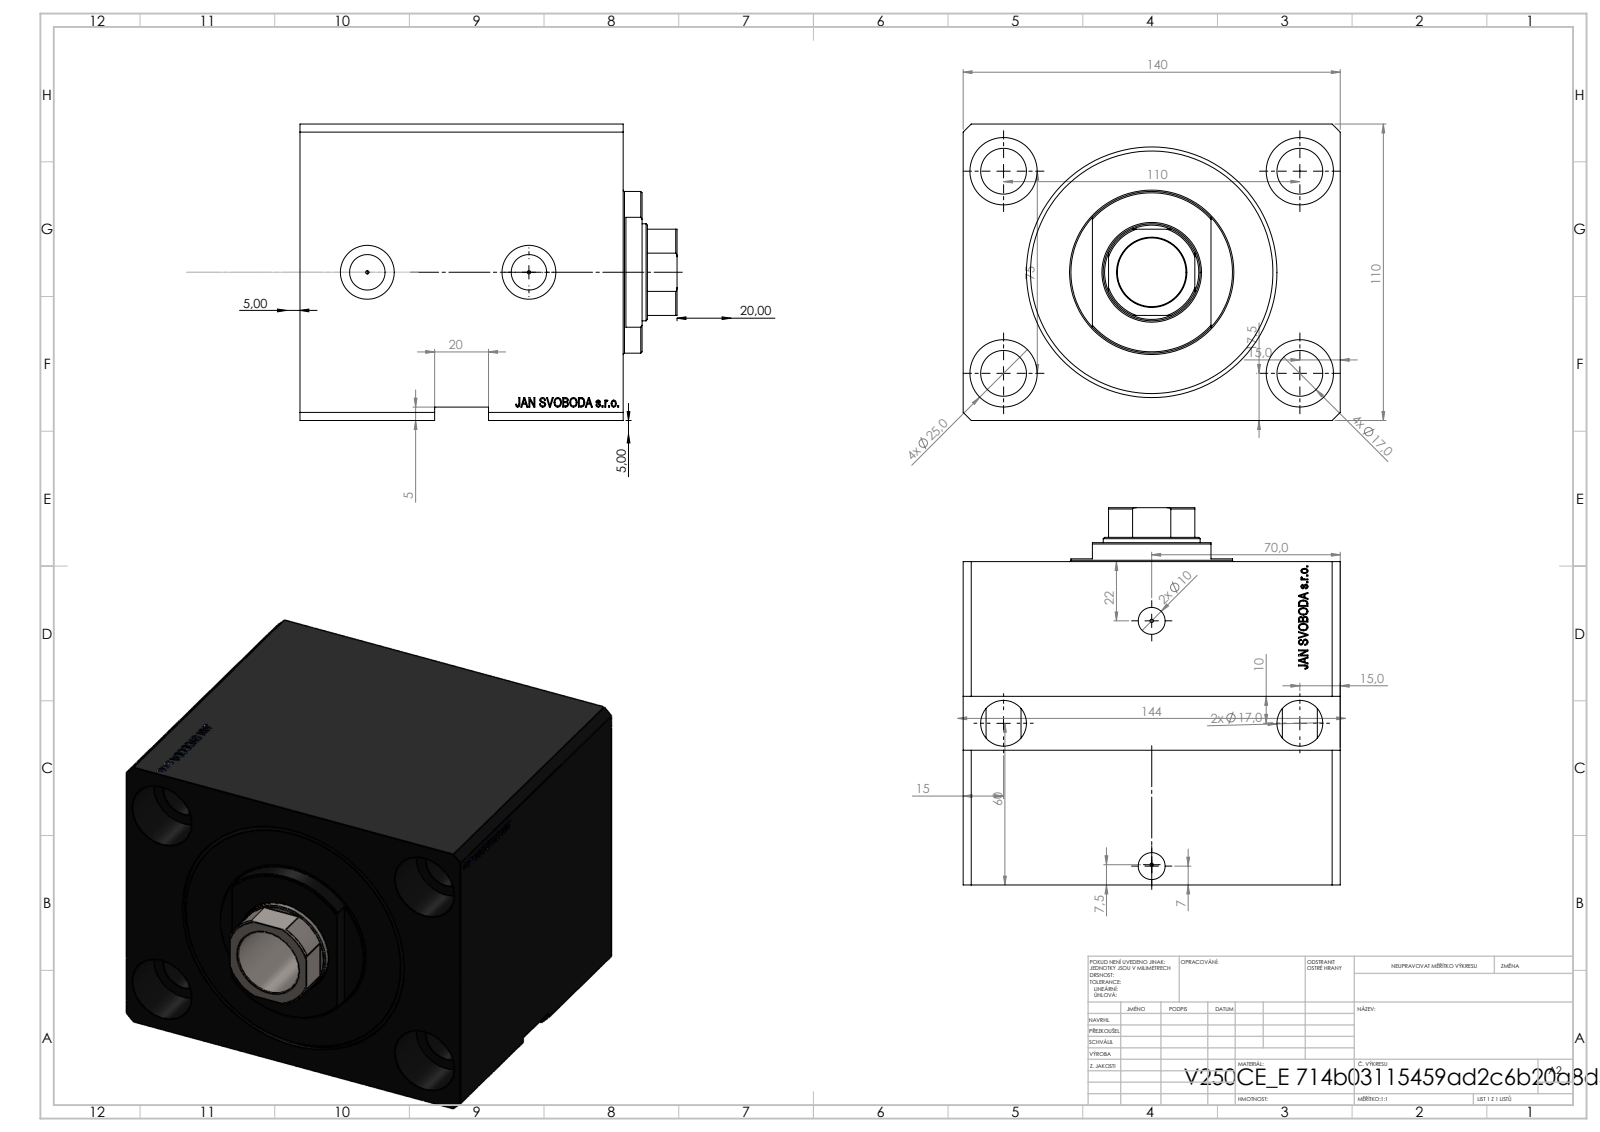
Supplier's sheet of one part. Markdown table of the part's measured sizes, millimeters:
| quantity | value |
| --- | --- |
| part name | V250CE_E_Body; V250CE_C_VCP; V250CE_VC_E |
| STEP written by | SolidWorks 2019 (CONFIG_CONTROL_DESIGN) |
| units | millimeters |
| bodies | 3 solids, 942 faces (472 planar, 84 cylindrical, 386 other) |
| overall size | 140 × 140 × 110 |
| volume | 1 577 000 mm³ |
| surface area | 209 983 mm² |
| round holes (diameter × count) | 17 × 6, 1.25 × 4, 25 × 4, 10 × 2, 13.16 × 2, 20 × 2, 25.5 × 1, 36 × 1, 80 × 1, 93 × 1 |
| round bosses / shafts (diameter × count) | 60 × 1 |
| partial cylindrical surfaces (radius × count) | 17.5 × 1 |
| main face-to-face distances | 110, 140, 25, 120, 95, 33, 62, 87, 53, 20 |
| hole center spacings | 66.57, 110, 66.85, 75, 76.01, 76.38, 133.14, 0.53 |
